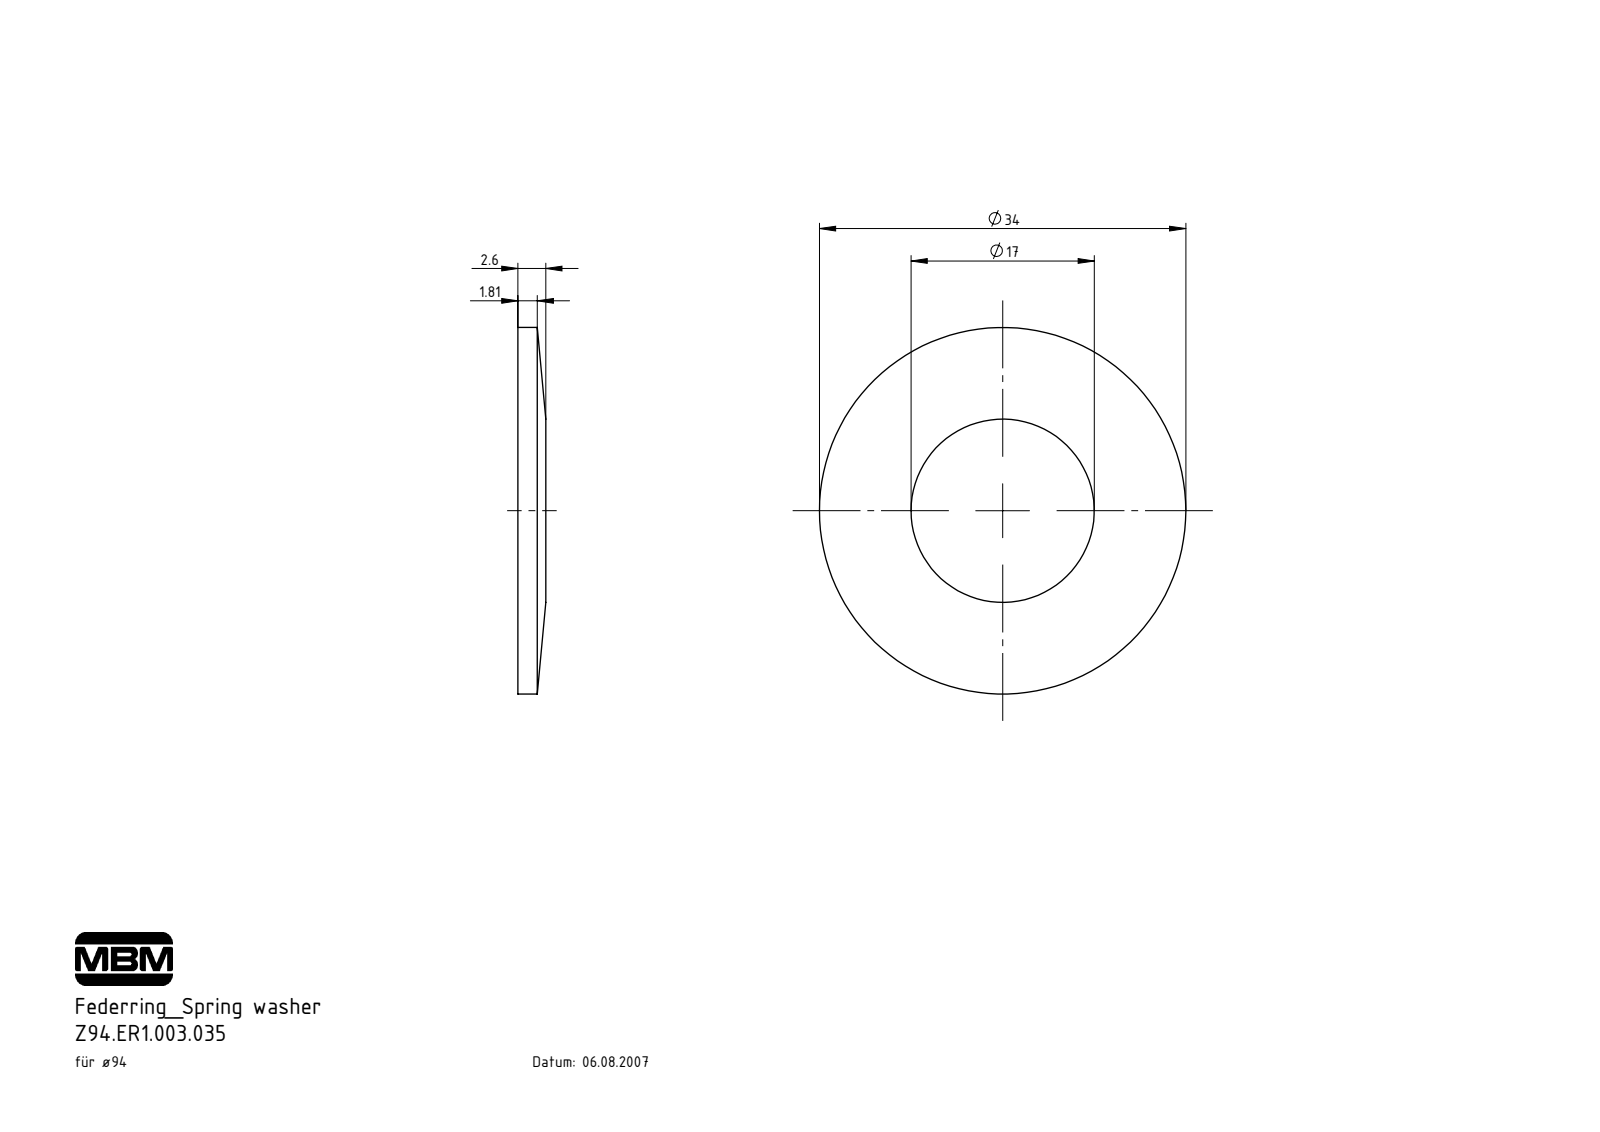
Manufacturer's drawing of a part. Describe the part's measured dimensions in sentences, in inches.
The part is named "Z94.ER1.003.035". Its 3-D file was written by "SolidWorks 2017 (AUTOMOTIVE_DESIGN)". It is 1 solid with 6 faces: 2 planar, 4 cylindrical and 0 other. Overall it measures 1.339 by 1.339 by 0.071 inches. Its volume is 0.075 cubic inches and its surface area 2.558 square inches. Round holes: 1 of diameter 0.669. Round bosses or shafts: 1 of diameter 1.339. The main face-to-face distances are 0.071.
